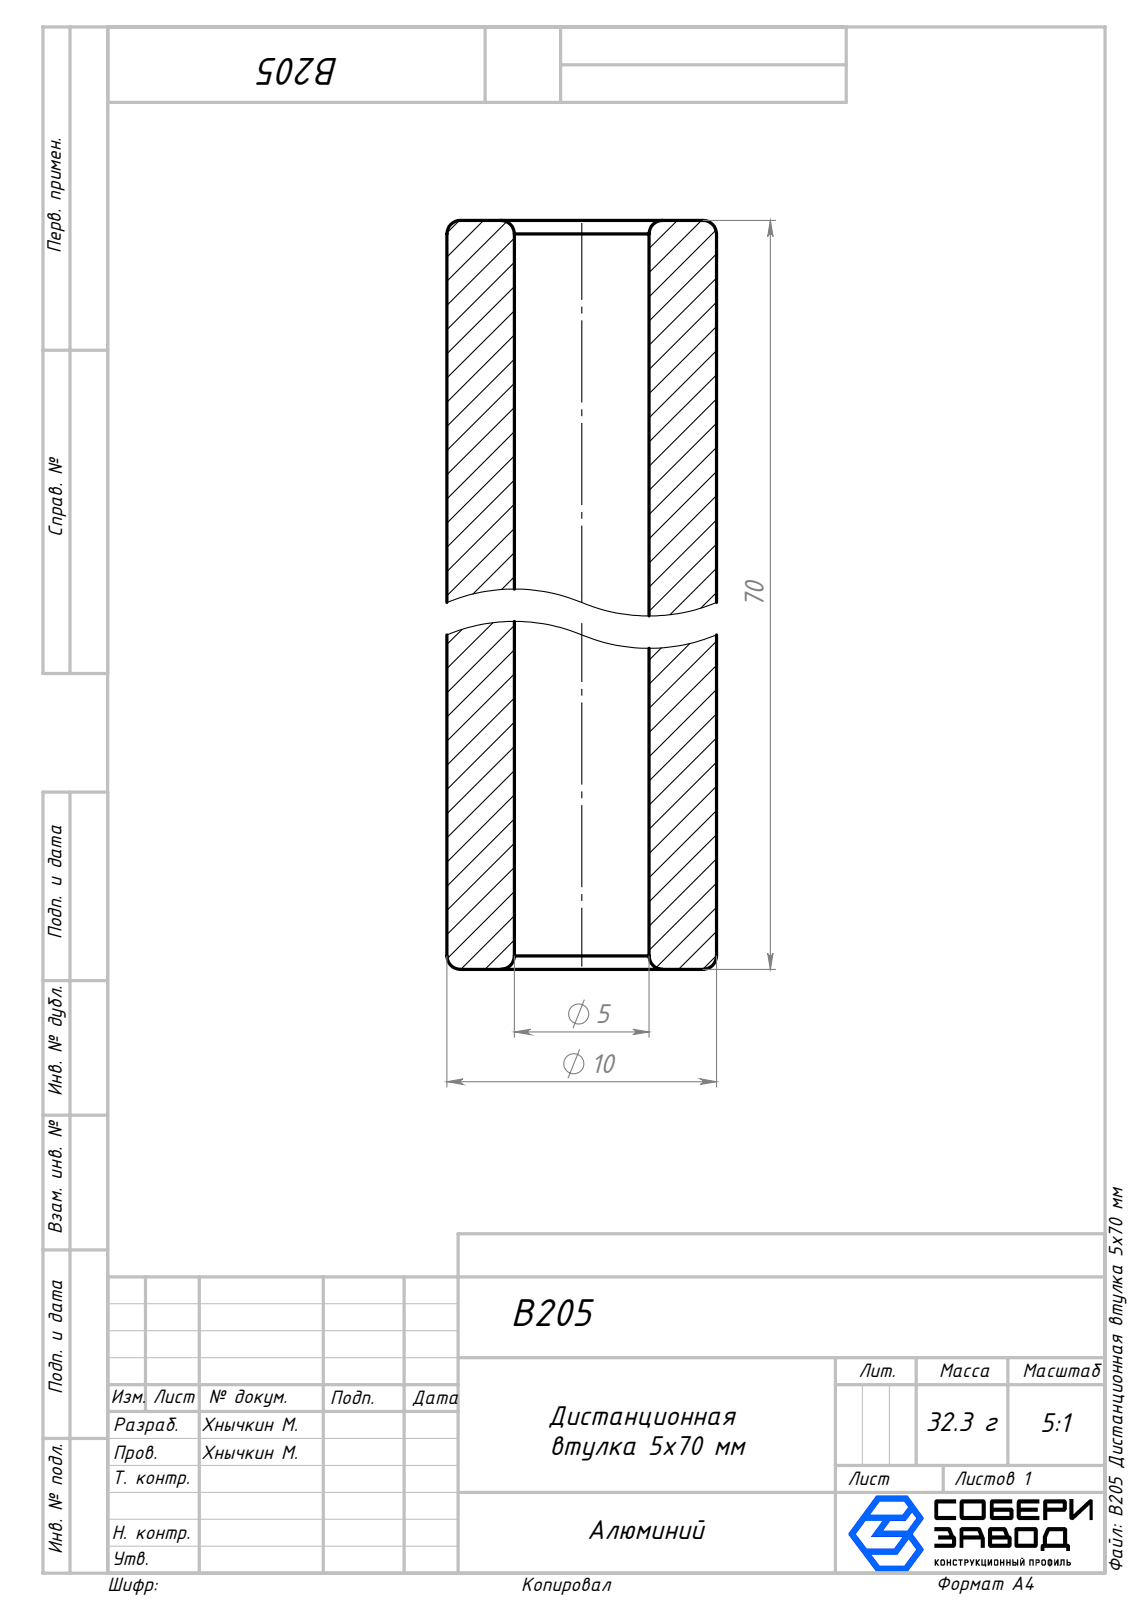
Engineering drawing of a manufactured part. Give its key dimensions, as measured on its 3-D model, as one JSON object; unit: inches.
{"part_name": "B205 Дистанционная втулка 5x70 мм", "step_written_by": "SolidWorks 2026 (AUTOMOTIVE_DESIGN)", "units": "inches", "bodies": {"solids": 1, "faces": 14, "planar": 2, "cylindrical": 4, "other": 8}, "overall_size": [2.756, 0.394, 0.394], "volume_in3": 0.251, "surface_area_in2": 5.264, "round_holes": [[0.197, 1]], "round_bosses_or_shafts": [[0.394, 1]], "face_to_face_distances": [2.756]}
